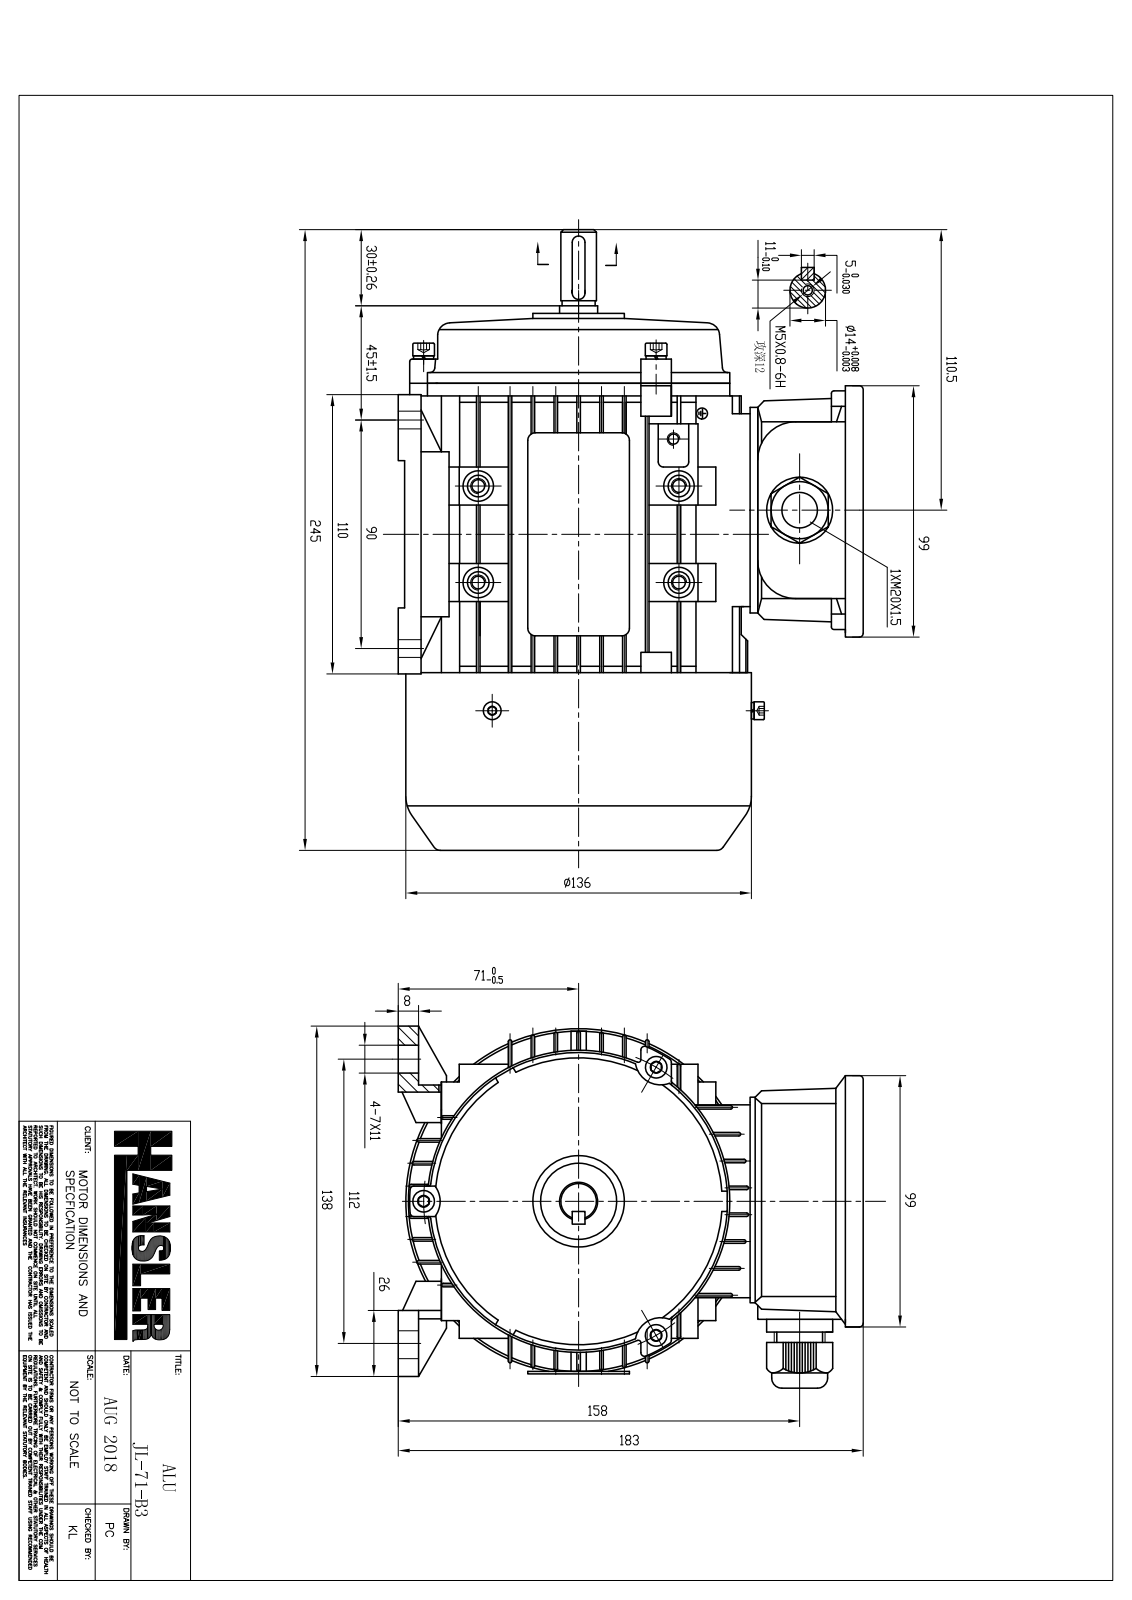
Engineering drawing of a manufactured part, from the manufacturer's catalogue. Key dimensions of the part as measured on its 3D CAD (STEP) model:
Part name (STEP PRODUCT): JL-71-B3
STEP written by: SIEMENS PLM Software NX 12.0 (AP203_CONFIGURATION_CONTROLLED_3D_DESIGN_OF_MECHANICAL_PARTS_AND_ASSEMBLIES_MIM_LF)
Units: millimetres
Bodies: 52 solids, 4149 faces (2425 planar, 1207 cylindrical, 517 other)
Overall size (bounding box): 245 × 183 × 140.1
Volume: 630 929 mm³ · Surface area: 496 058 mm²
Round holes (diameter × count): ⌀4 ×13, ⌀5.8 ×13, ⌀5 ×12, ⌀12 ×10, ⌀3.5 ×6, ⌀4.25 ×6, ⌀5.25 ×5, ⌀4.13 ×4, ⌀6.7 ×4, ⌀9 ×4, ⌀3.2 ×3, ⌀4.9 ×3
Round bosses / shafts (diameter × count): ⌀8.5 ×8, ⌀5 ×7, ⌀6.45 ×6, ⌀3.55 ×6, ⌀7.85 ×5, ⌀4.48 ×5, ⌀13 ×4, ⌀12 ×4
Partial cylindrical surfaces — rounded edges, fillets, slot ends (radius × count): R0.5 ×336, R1 ×49, R2 ×36, R1.5 ×28, R5 ×17, R0.6 ×14, R4 ×12, R2.5 ×8
Main face-to-face distances: 10.57, 2, 21.14, 1.4, 31.71, 9.17, 11.97, 42.28, 41, 19.74
Hole centre spacings: 15.81, 29.15, 31.91, 43.68, 45.8, 49.93, 52.8, 63.07
